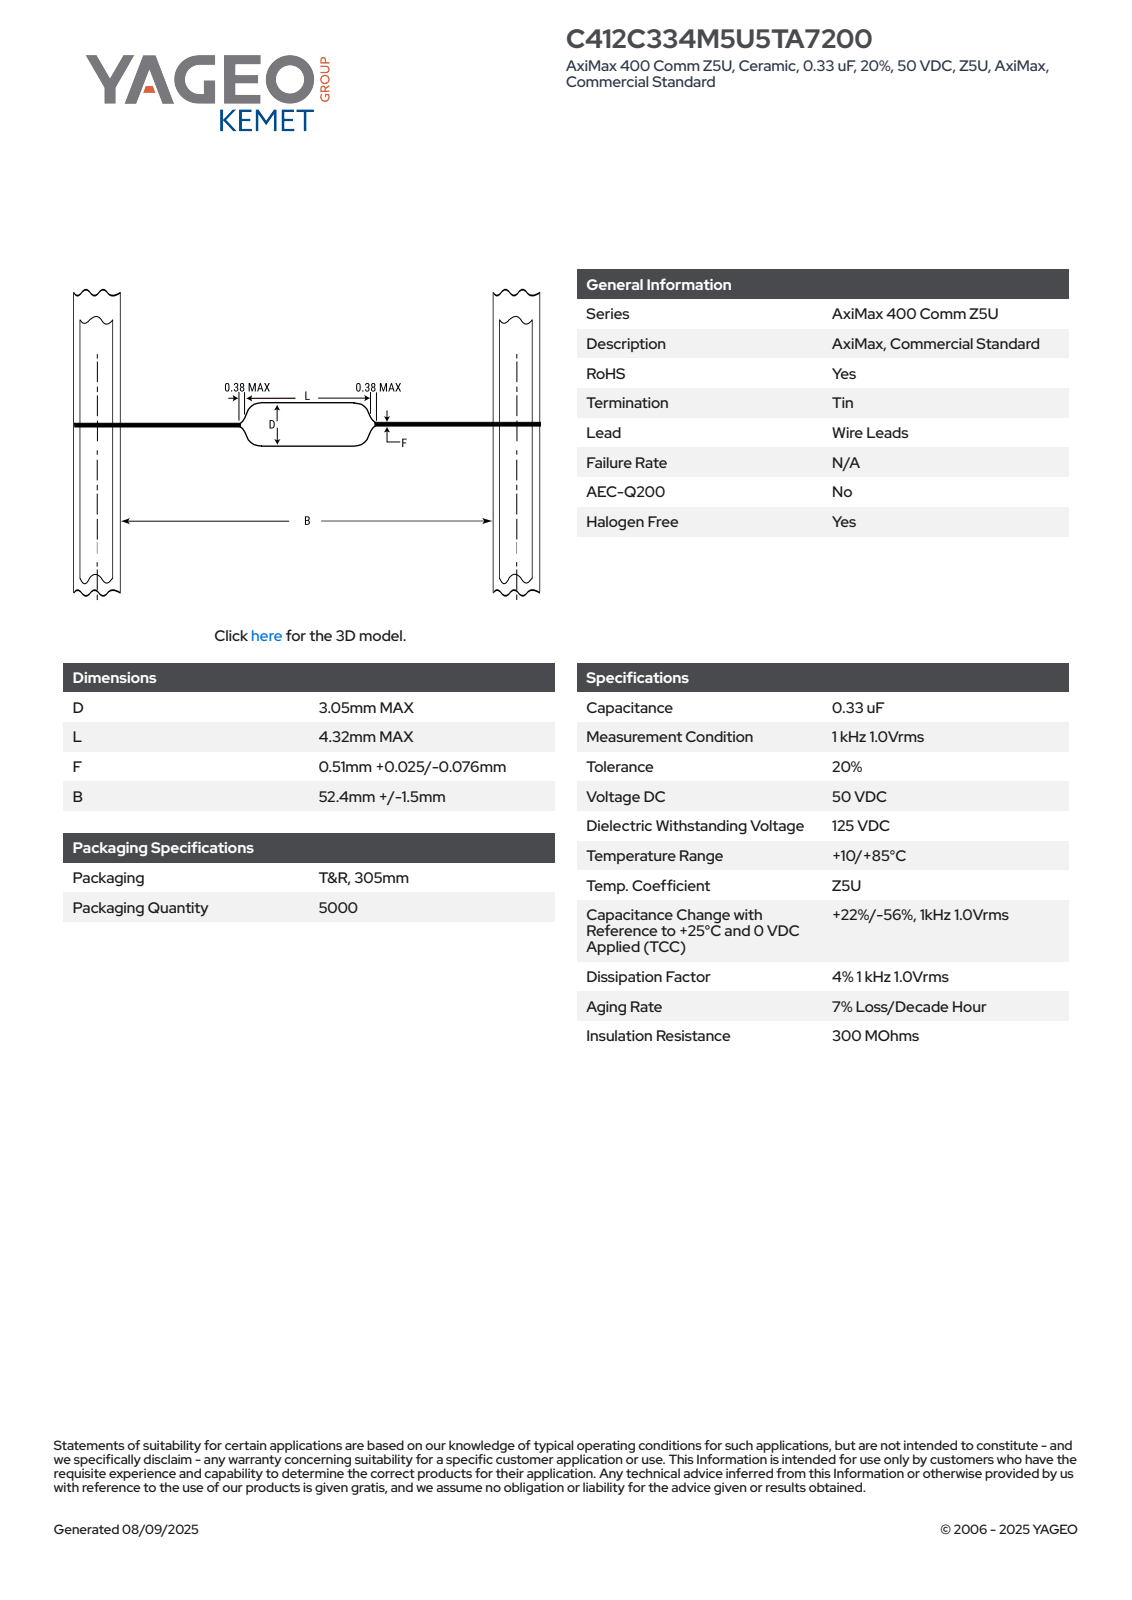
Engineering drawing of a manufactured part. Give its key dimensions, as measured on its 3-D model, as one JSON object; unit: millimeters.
{"part_name": "CCA_ACSTTAPE_C412_D3.05L4.32LL25.4F0.535", "step_written_by": "SolidWorks 2014 (AUTOMOTIVE_DESIGN)", "units": "millimeters", "bodies": {"solids": 1, "faces": 74, "planar": 26, "cylindrical": 9, "other": 39}, "overall_size": [55.88, 3.05, 3.05], "volume_mm3": 42, "surface_area_mm2": 137, "round_bosses_or_shafts": [[3.05, 1], [0.54, 1]], "partial_cylinders_radius": [[1.51, 1]], "face_to_face_distances": [4.32, 25.78, 30.1, 55.88]}
